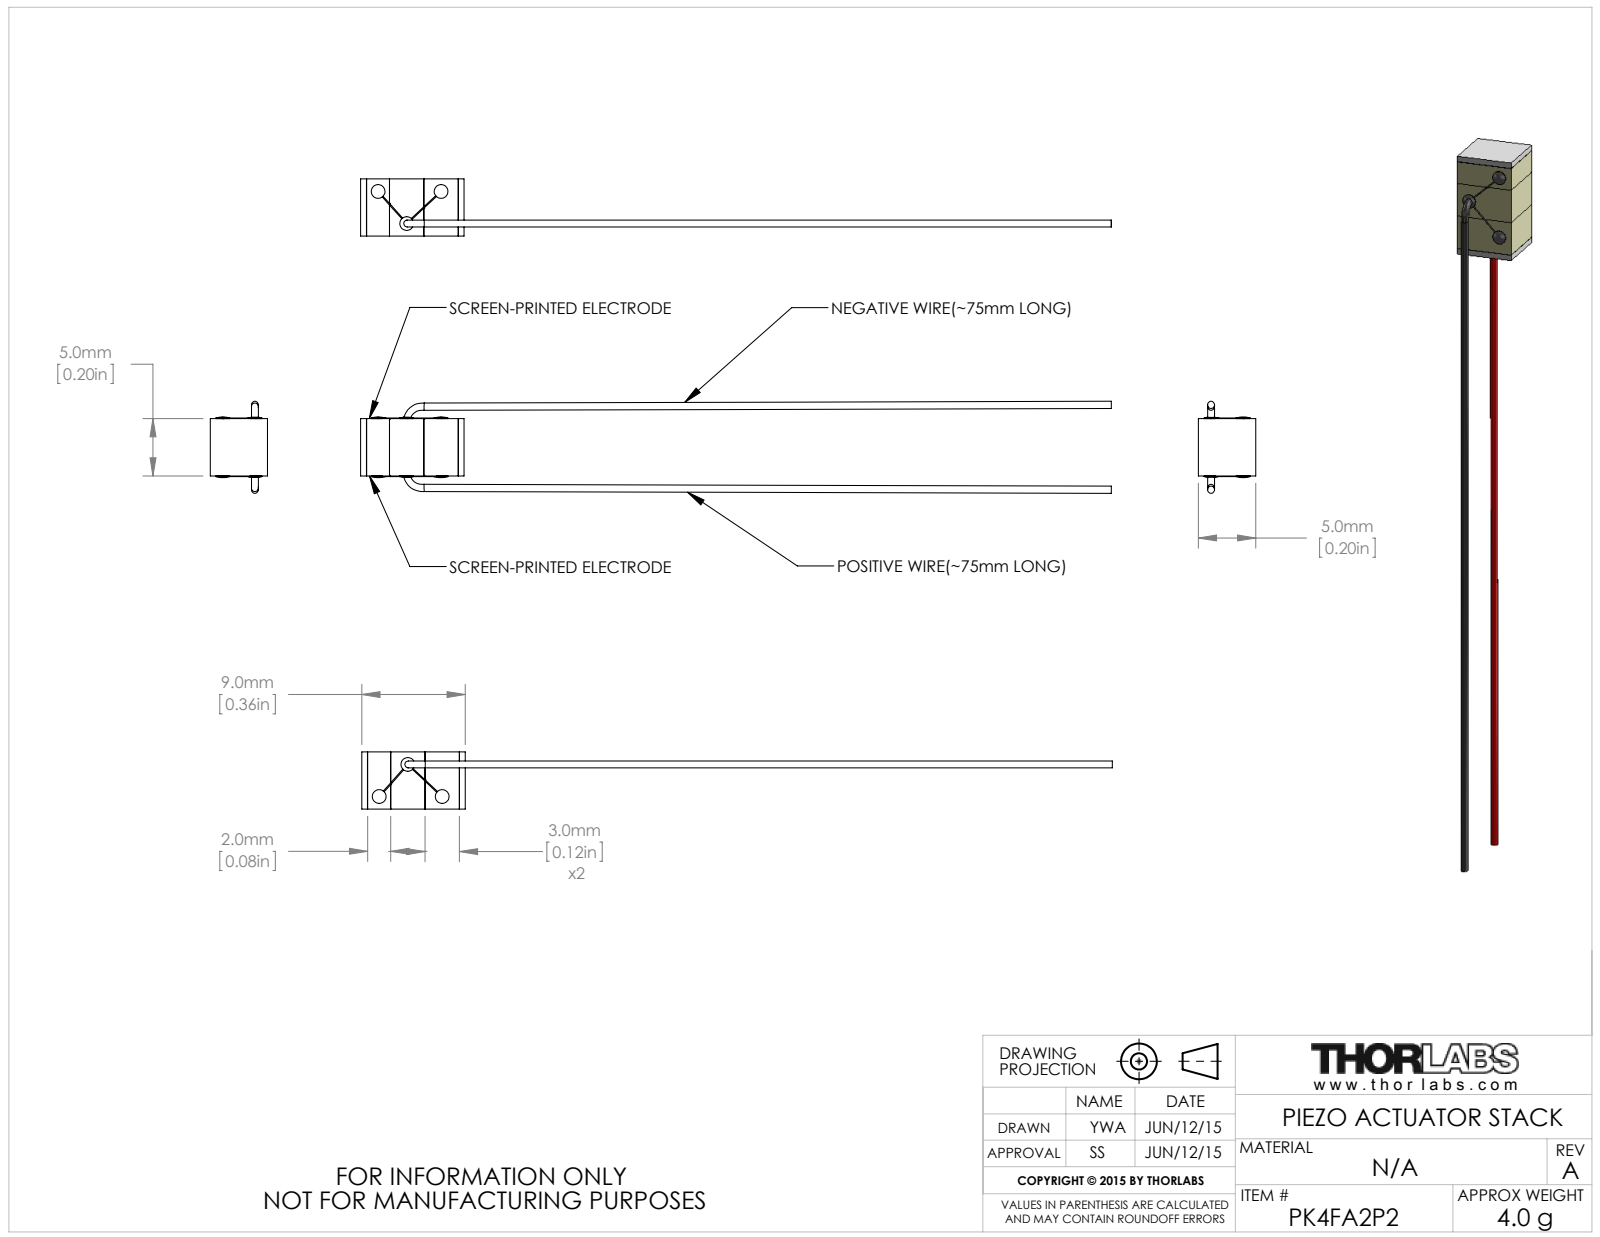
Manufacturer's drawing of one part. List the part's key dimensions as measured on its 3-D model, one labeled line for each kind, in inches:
Part name (STEP PRODUCT): CTN003149
STEP written by: SolidWorks 2014 (AUTOMOTIVE_DESIGN)
Units: inches
Bodies: 3 solids, 86 faces (46 planar, 20 cylindrical, 20 other)
Overall size (bounding box): 2.58 × 0.316 × 0.197
Volume: 0.016 in³ · Surface area: 1.06 in²
Round bosses / shafts (diameter × count): ⌀0.047 ×3
Main face-to-face distances: 0.197, 0.118, 0.02, 0.336, 0.138, 0.256, 0.335, 0.356, 0.119, 0.237
